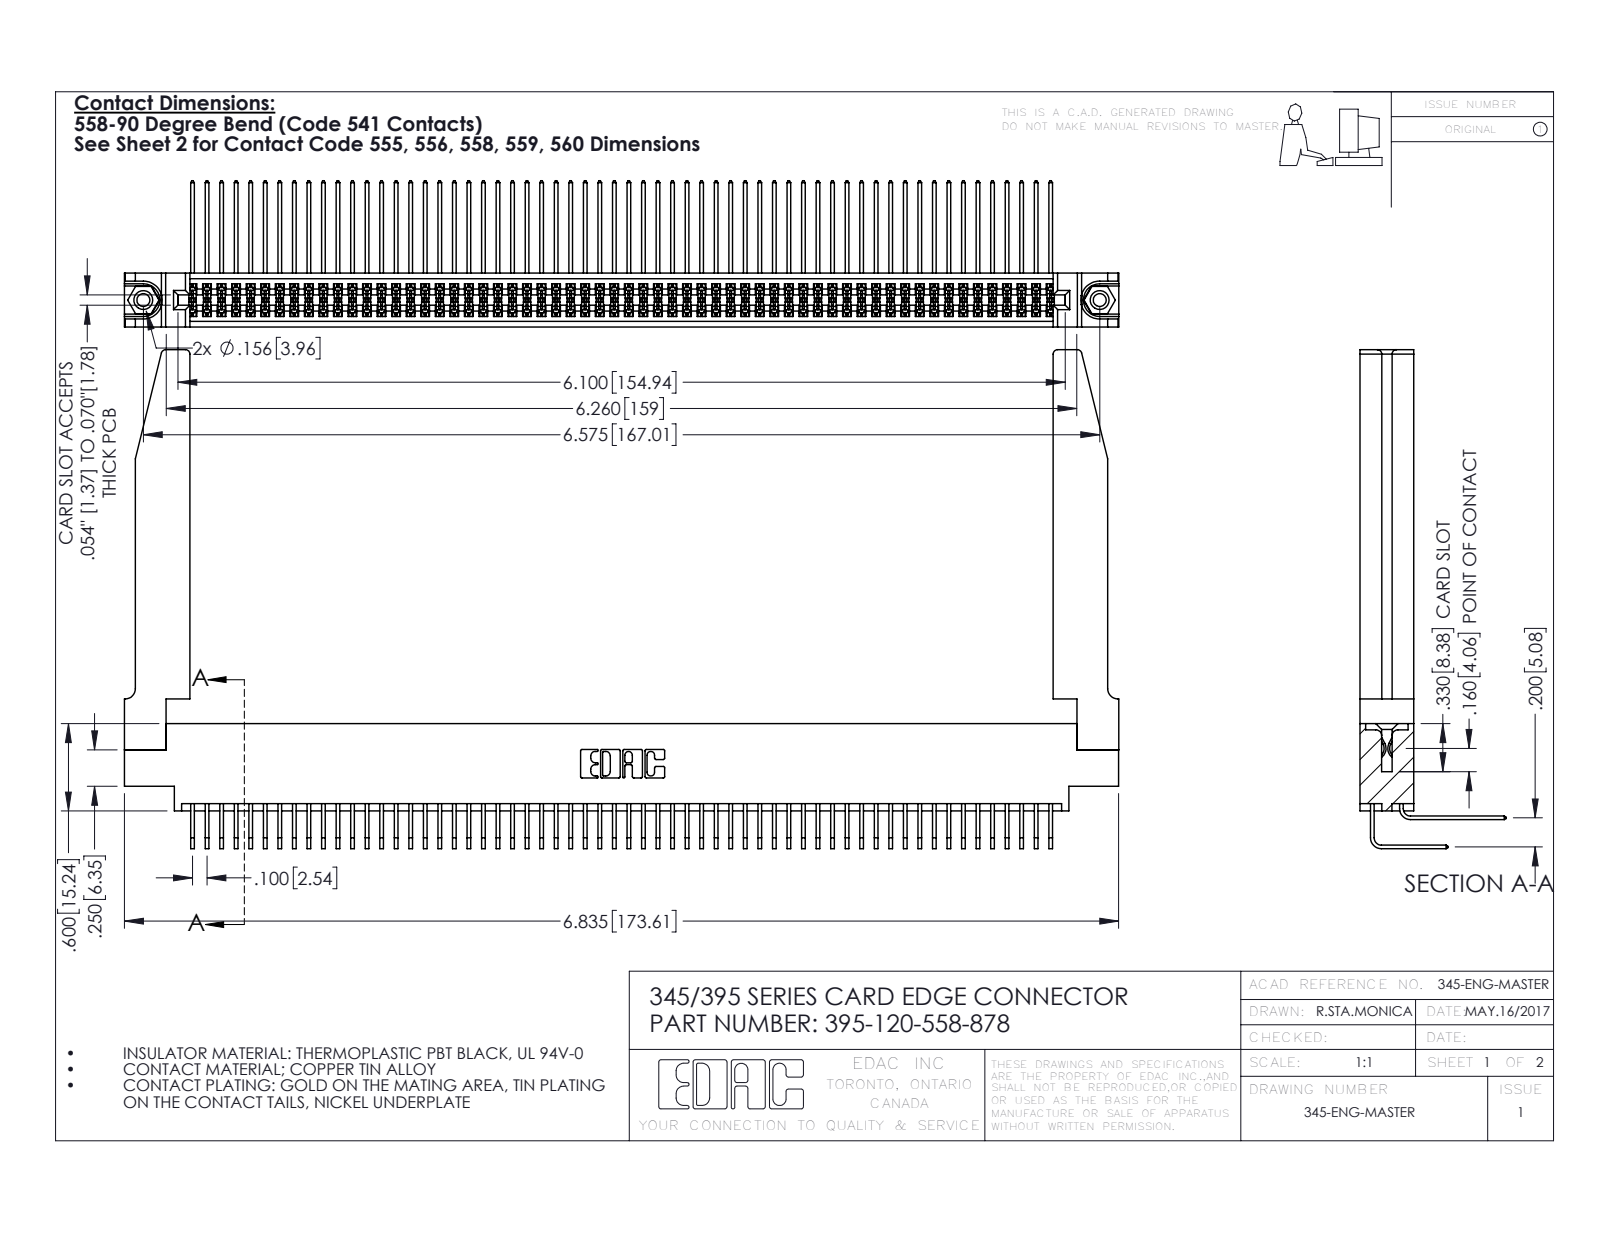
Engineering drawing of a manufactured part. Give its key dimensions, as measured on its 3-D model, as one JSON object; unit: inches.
{"part_name": "395-120-558-878; 345-220-078_345-220-078; 345 Part_0.170 Offset - 0.156 Dia-TH; 345-250-001_345-250-001-102 (+2 more)", "step_written_by": "SolidWorks 2016 (CONFIG_CONTROL_DESIGN)", "units": "inches", "bodies": {"solids": 125, "faces": 6604, "planar": 4426, "cylindrical": 2126, "other": 52}, "overall_size": [6.836, 3.429, 1.005], "volume_in3": 1.549, "surface_area_in2": 56.76, "round_holes": [[0.089, 2], [0.125, 2], [0.156, 2], [0.064, 1]], "round_bosses_or_shafts": [[0.155, 2]], "partial_cylinders_radius": [[0.006, 181], [0.01, 22], [0.03, 8], [0.007, 6], [0.031, 6], [0.026, 3], [0.014, 2], [0.019, 2]], "face_to_face_distances": [0.072, 0.298, 0.37, 0.2, 0.098, 0.272, 0.025, 0.225, 0.175, 0.025], "hole_center_spacings": [0.27, 6.339, 6.575]}
